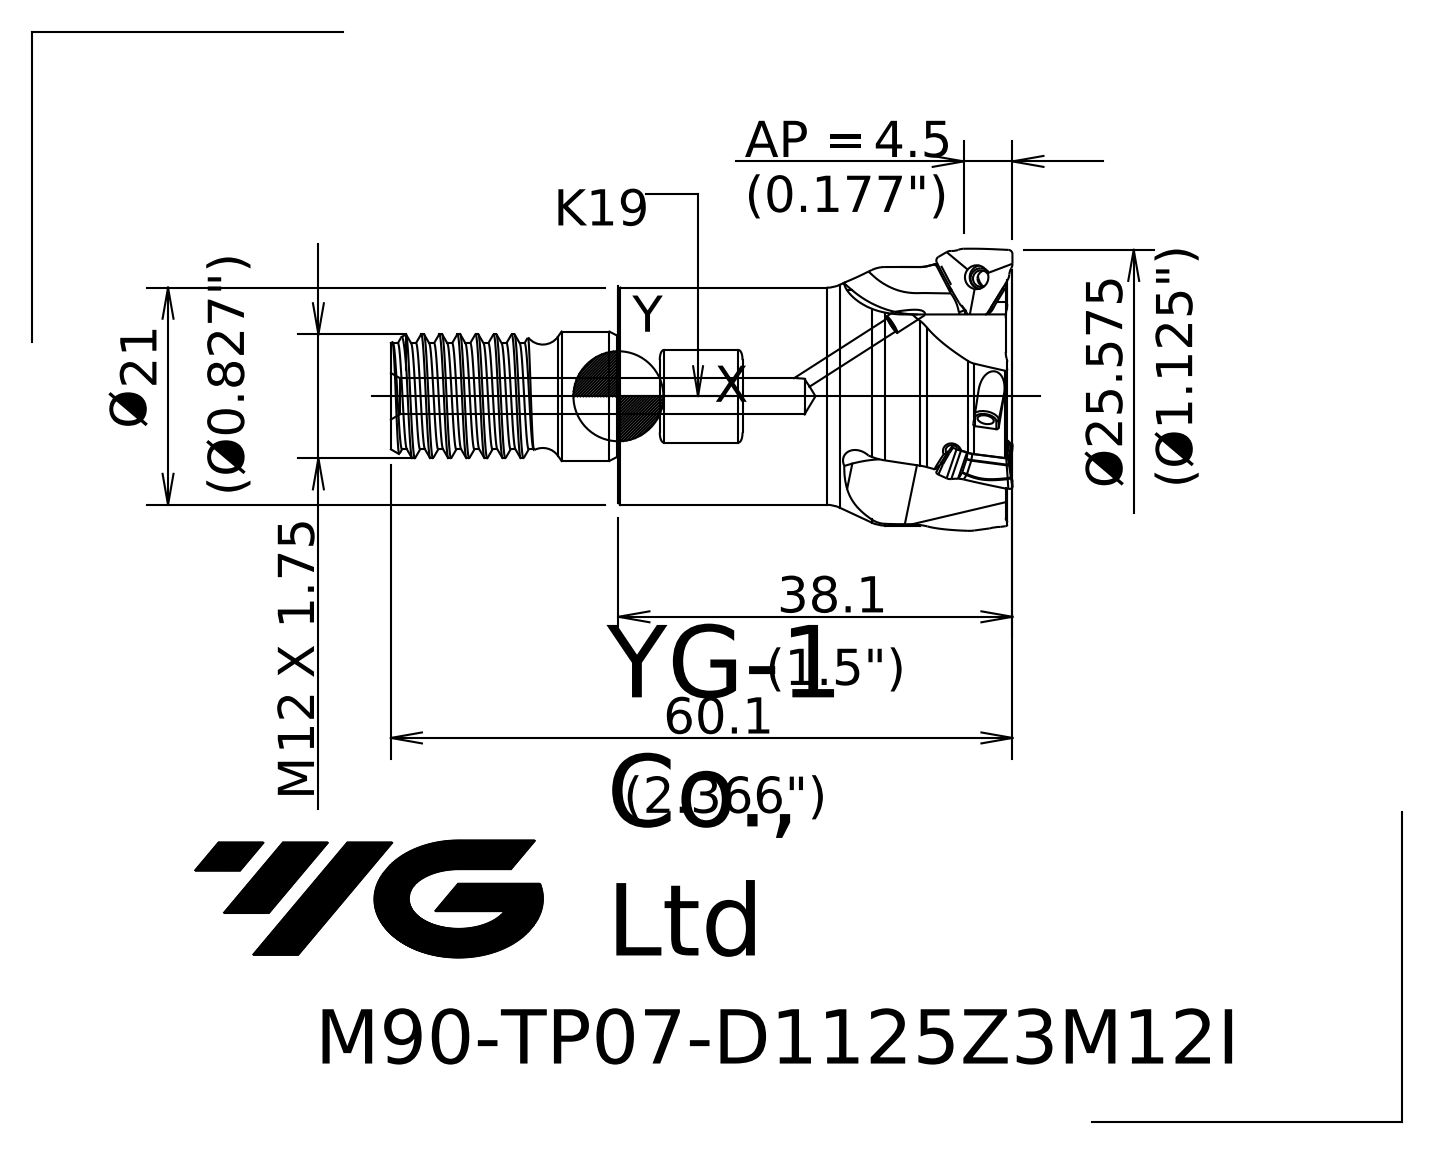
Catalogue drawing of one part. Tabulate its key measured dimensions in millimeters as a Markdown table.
| quantity | value |
| --- | --- |
| part name | 10225690B4FA62tl |
| STEP written by | SIEMENS PLM Software NX 10.0 (AP203_CONFIGURATION_CONTROLLED_3D_DESIGN_OF_MECHANICAL_PARTS_AND_ASSEMBLIES_MIM_LF) |
| units | millimeters |
| bodies | 1 solid, 69 faces (12 planar, 11 cylindrical, 46 other) |
| overall size | 60.1 × 28.63 × 28.63 |
| volume | 17 268 mm³ |
| surface area | 6 816 mm² |
| round holes (diameter × count) | 1.5 × 1, 3.5 × 1 |
| round bosses / shafts (diameter × count) | 25 × 1, 21 × 1, 12.5 × 1, 12 × 1, 10.25 × 1 |
| partial cylindrical surfaces (radius × count) | 0.4 × 4 |
| main face-to-face distances | 37.45, 59.45, 22, 19, 37.6, 59.6, 25.6, 25.45, 12, 34 |
